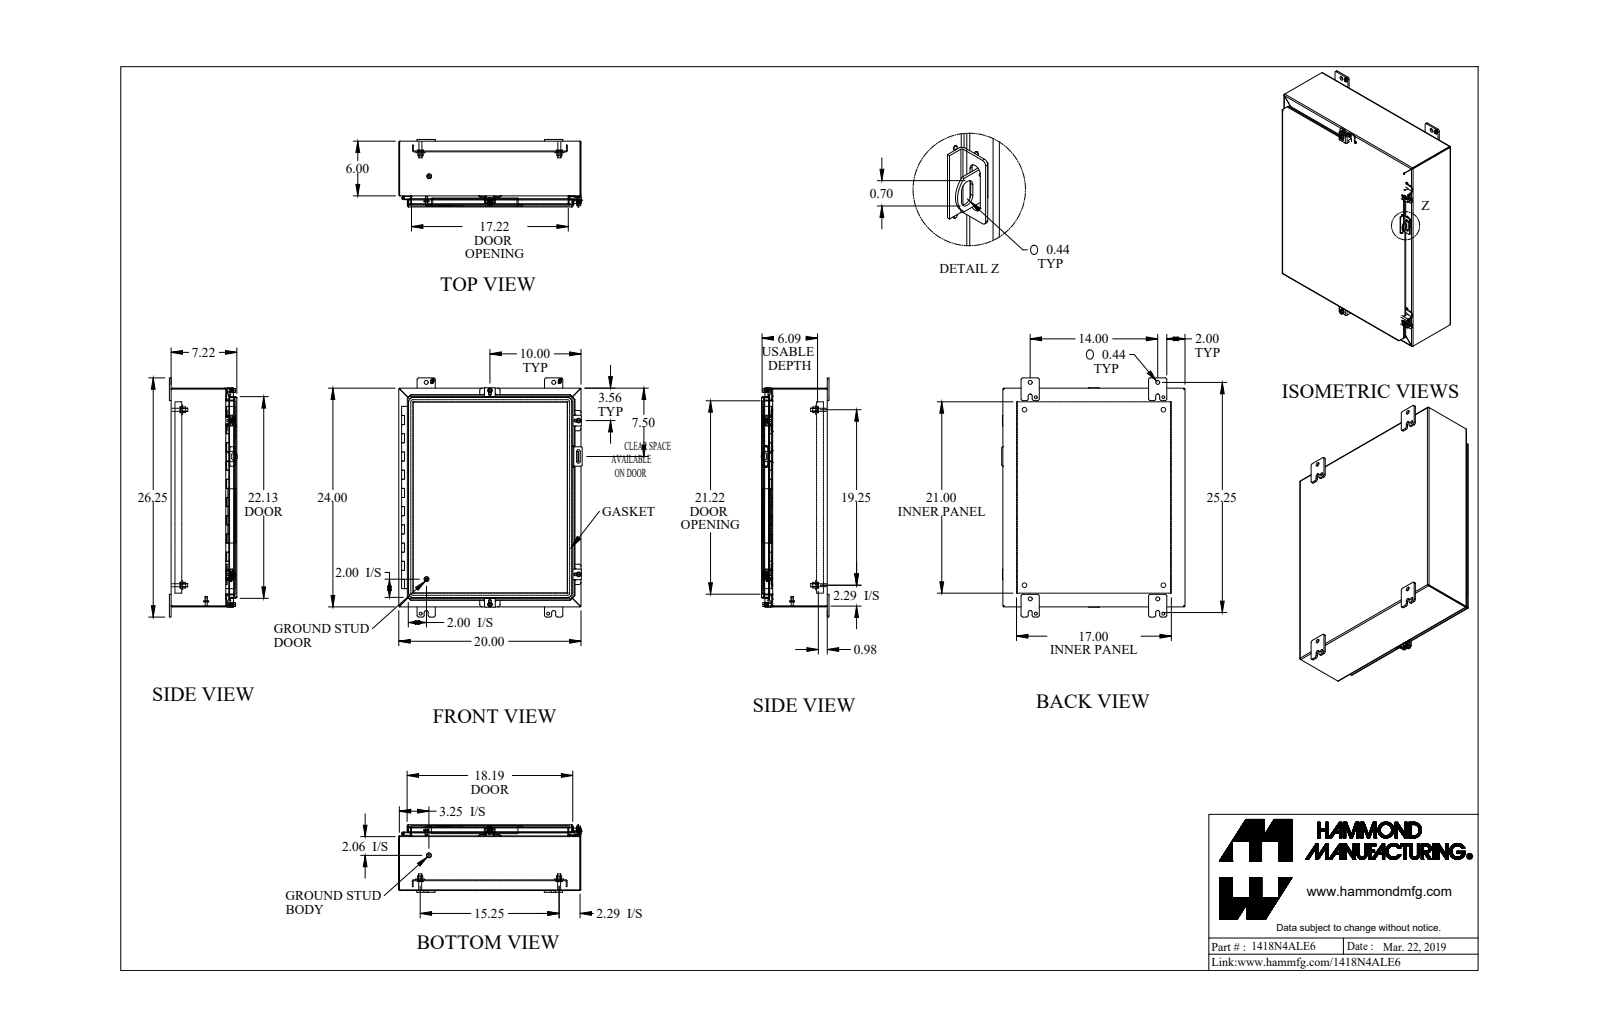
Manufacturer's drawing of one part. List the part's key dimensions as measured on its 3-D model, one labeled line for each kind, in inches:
Part name (STEP PRODUCT): 1418N4ALE6_Default
STEP written by: SolidWorks 2019 (CONFIG_CONTROL_DESIGN)
Units: inches
Bodies: 38 solids, 1524 faces (899 planar, 515 cylindrical, 110 other)
Overall size (bounding box): 26.25 × 20.126 × 7.437
Volume: 196.5 in³ · Surface area: 4 506 in²
Round holes (diameter × count): ⌀0.232 ×4, ⌀0.313 ×4, ⌀0.375 ×4, ⌀0.437 ×4, ⌀0.5 ×4, ⌀0.265 ×2, ⌀0.265 ×2, ⌀0.307 ×2, ⌀0.445 ×2, ⌀0.125 ×1, ⌀0.187 ×1
Round bosses / shafts (diameter × count): ⌀0.131 ×12, ⌀0.65 ×4, ⌀0.5 ×4, ⌀0.4 ×4, ⌀0.375 ×4, ⌀0.33 ×4, ⌀0.244 ×4, ⌀1 ×2
Partial cylindrical surfaces — rounded edges, fillets, slot ends (radius × count): R0.188 ×24, R0.05 ×22, R0.15 ×22, R0.25 ×20, R0.041 ×16, R0.122 ×16, R0.125 ×10, R0.141 ×8
Main face-to-face distances: 0.081, 0.1, 7.041, 7.122, 7.141, 7.222, 0.095, 6.046, 5.946, 1.095
Hole centre spacings: 14, 22.694, 7.915, 7.916, 15.25, 17.415, 24.559, 1.625
